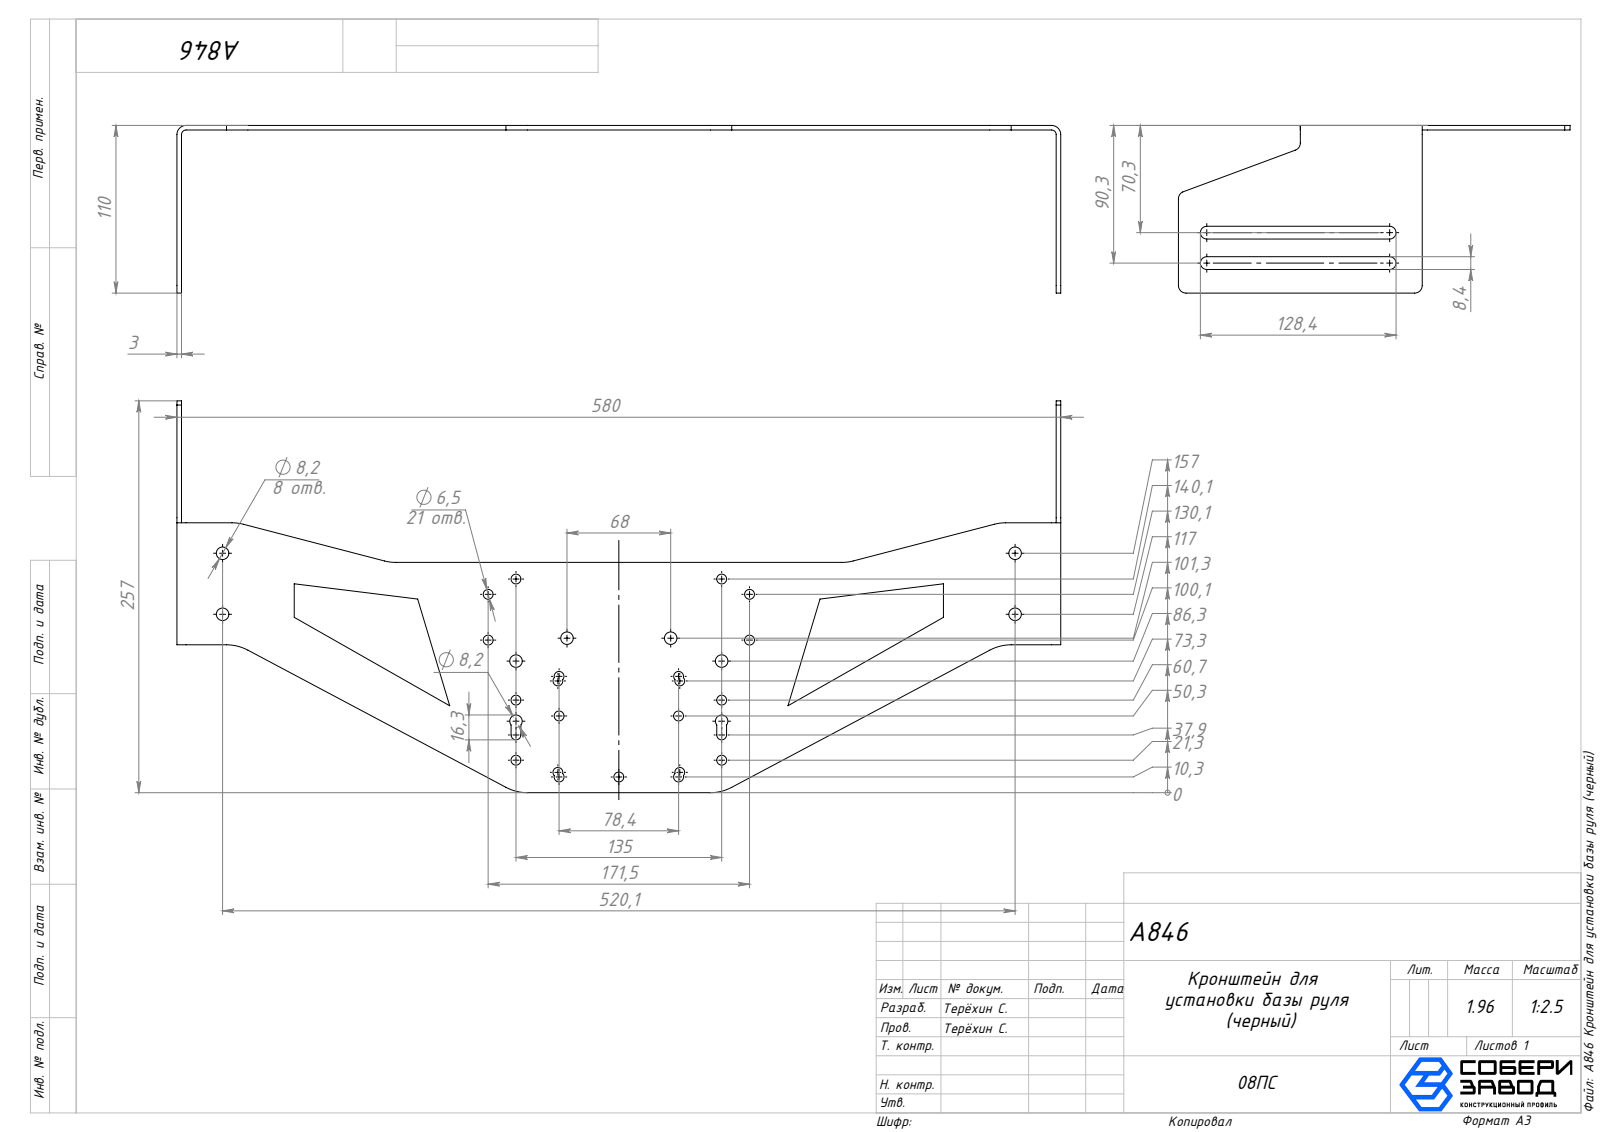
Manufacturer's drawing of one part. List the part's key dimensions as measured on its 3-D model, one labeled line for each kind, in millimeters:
Part name (STEP PRODUCT): A814 Кронштейн для установки базы руля
STEP written by: SolidWorks 2025 (AUTOMOTIVE_DESIGN)
Units: millimetres
Bodies: 1 solid, 153 faces (48 planar, 103 cylindrical, 2 other)
Overall size (bounding box): 580 × 257.02 × 109.99
Volume: 249 586 mm³ · Surface area: 179 501 mm²
Round holes (diameter × count): ⌀6.48 ×4, ⌀6.51 ×4, ⌀8.25 ×4, ⌀6.49 ×2, ⌀6.53 ×2, ⌀8.21 ×2, ⌀8.25 ×2, ⌀6.52 ×1
Partial cylindrical surfaces — rounded edges, fillets, slot ends (radius × count): R4.2 ×4, R3 ×2, R3.21 ×2, R3.24 ×2, R3.24 ×2, R3.25 ×2, R3.28 ×2, R4.09 ×2
Main face-to-face distances: 3, 577, 574, 580, 8.4, 19.97, 106.99, 109.99, 54.04, 23.89
Hole centre spacings: 25.59, 30.02, 39.42, 40.04, 44.02, 51.28, 51.75, 53.83
